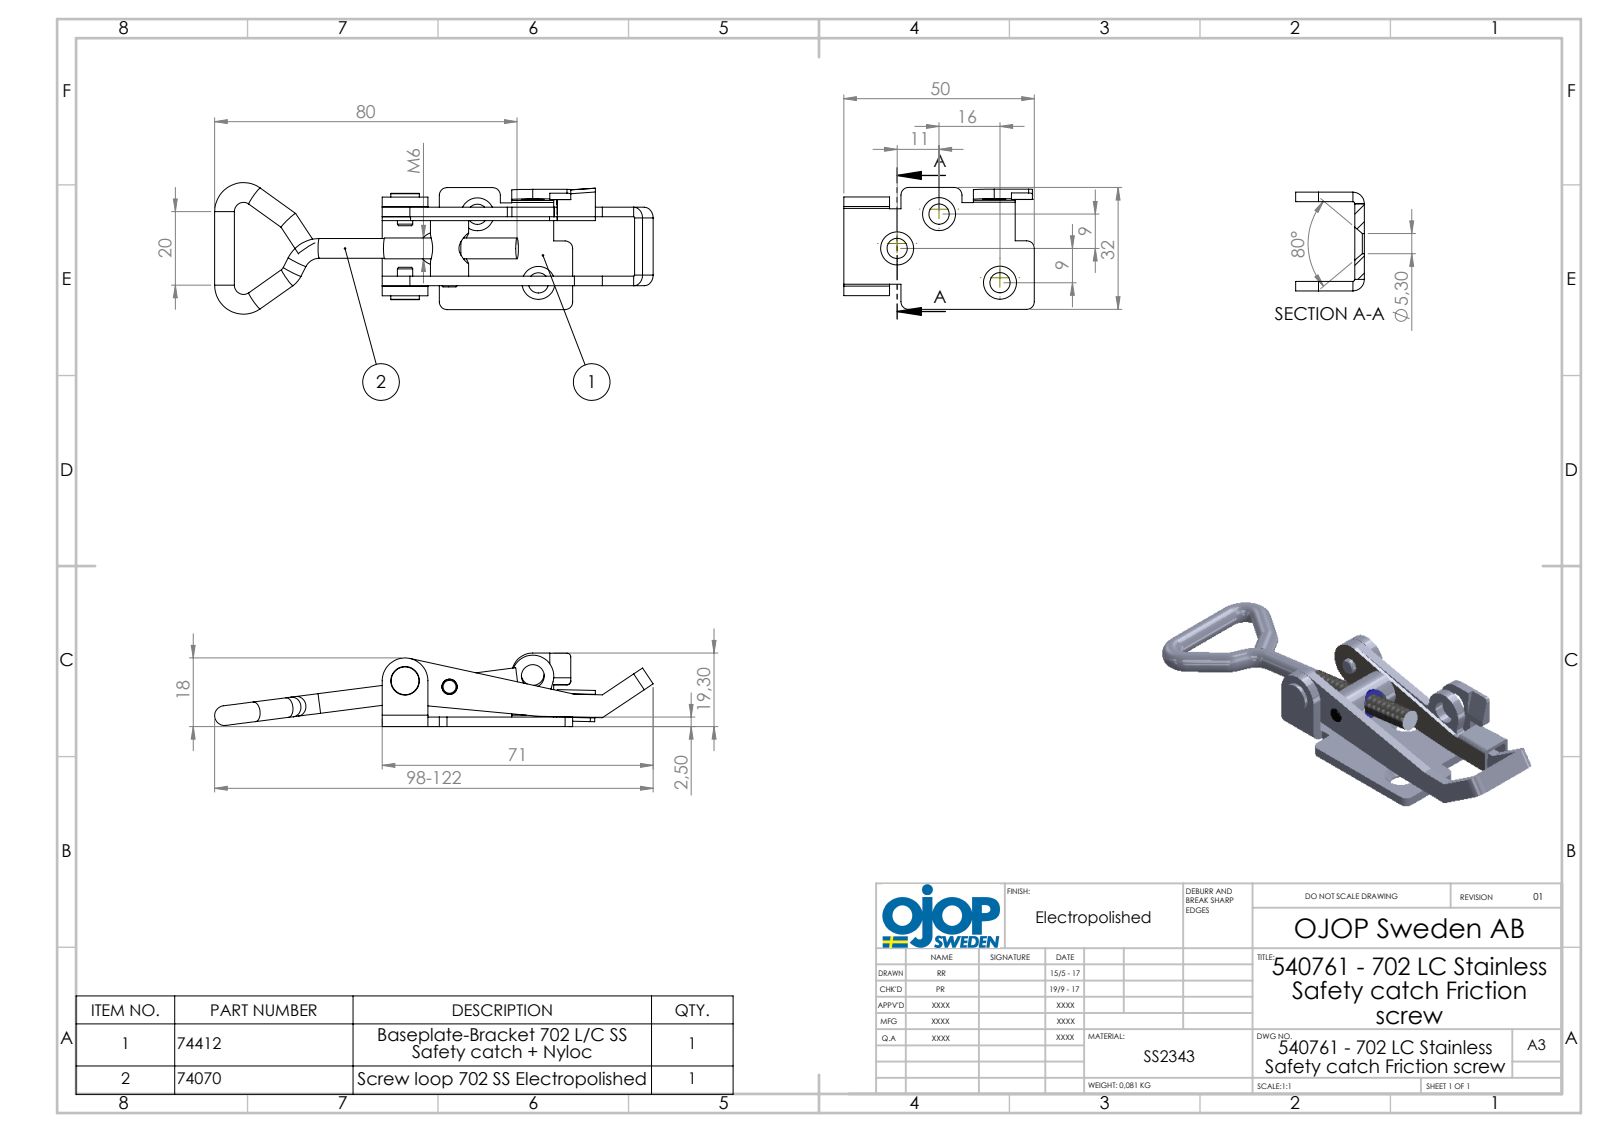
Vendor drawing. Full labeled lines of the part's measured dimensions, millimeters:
Part name (STEP PRODUCT): 702 - Platta LC Spärr; 540761 - 702 LC Stainless Safety catch Friction screw; 702 - Safety Catch; 702 - Bygel låsögla (+5 more)
STEP written by: SolidWorks 2015 (AUTOMOTIVE_DESIGN)
Units: millimetres
Bodies: 8 solids, 229 faces (97 planar, 102 cylindrical, 30 other)
Overall size (bounding box): 118.62 × 34.52 × 19.3
Volume: 12 350 mm³ · Surface area: 13 022 mm²
Round holes (diameter × count): ⌀5.3 ×3, ⌀6 ×3, ⌀4 ×2, ⌀4.1 ×2, ⌀5 ×1, ⌀5.1 ×1, ⌀8 ×1
Round bosses / shafts (diameter × count): ⌀5.18 ×6, ⌀10 ×1, ⌀7.5 ×1, ⌀5.5 ×1
Partial cylindrical surfaces — rounded edges, fillets, slot ends (radius × count): R1 ×11, R2 ×5, R0.5 ×3, R3 ×3, R0.3 ×2, R2.8 ×2, R5.5 ×2, R6 ×1
Main face-to-face distances: 2.5, 18.1, 1, 15.6, 3.5, 20.6, 14.6, 17.1, 23.4, 6.1
Hole centre spacings: 11.77, 14.21, 22.04, 24.08, 28.46, 33.55
